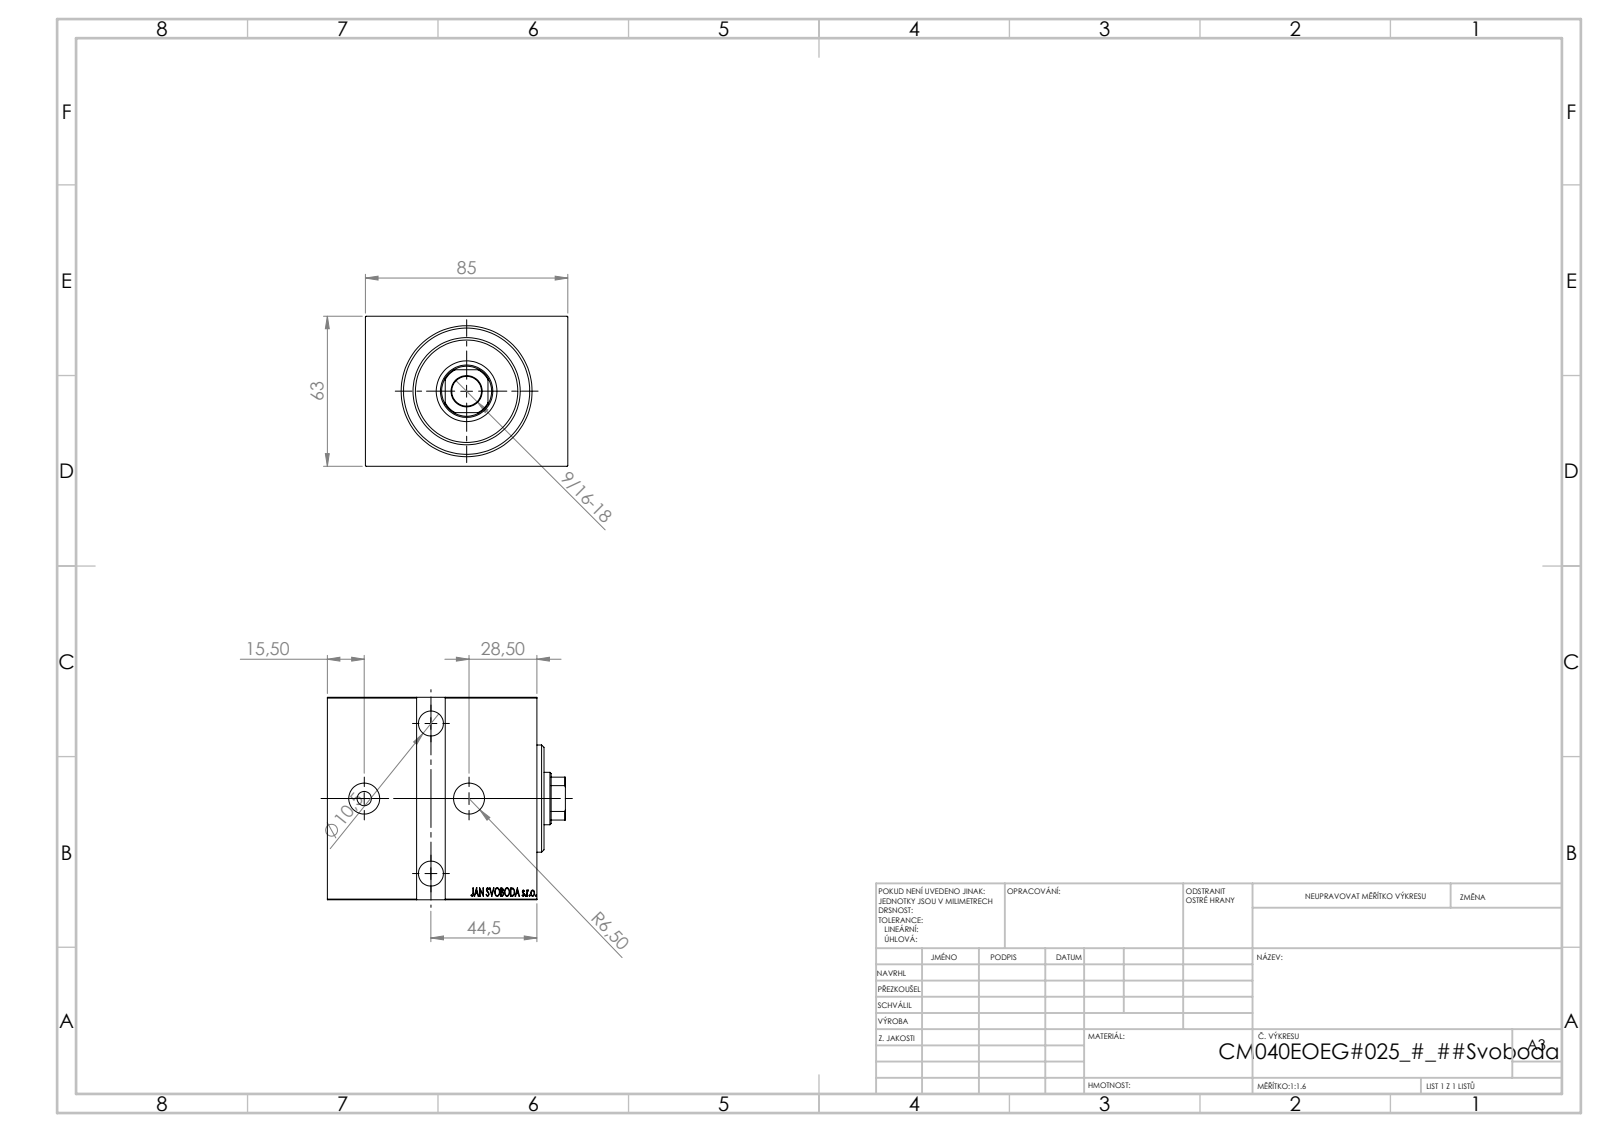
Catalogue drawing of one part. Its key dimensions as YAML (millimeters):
part_name: "V450CM_VC_B; V450CM_E_Body; V450CM_E_VCP"
step_written_by: "SolidWorks 2019 (CONFIG_CONTROL_DESIGN)"
units: millimeters
bodies: {solids: 3, faces: 839, planar: 407, cylindrical: 38, other: 394}
overall_size: [100, 85, 63]
volume: 443096
surface_area: 70806
round_holes:
  - {diameter: 10.5, count: 2}
  - {diameter: 13, count: 2}
  - {diameter: 16.5, count: 2}
  - {diameter: 12.5, count: 1}
  - {diameter: 22, count: 1}
  - {diameter: 25.5, count: 1}
  - {diameter: 40, count: 1}
  - {diameter: 53, count: 1}
round_bosses_or_shafts:
  - {diameter: 45, count: 1}
  - {diameter: 42, count: 1}
  - {diameter: 6, count: 1}
partial_cylinders:
  - {radius: 10.5, count: 1}
face_to_face_distances: [63, 85, 88, 12, 76, 3, 5, 83, 71, 18]
hole_center_spacings: [35.33, 42.15, 44, 63]
